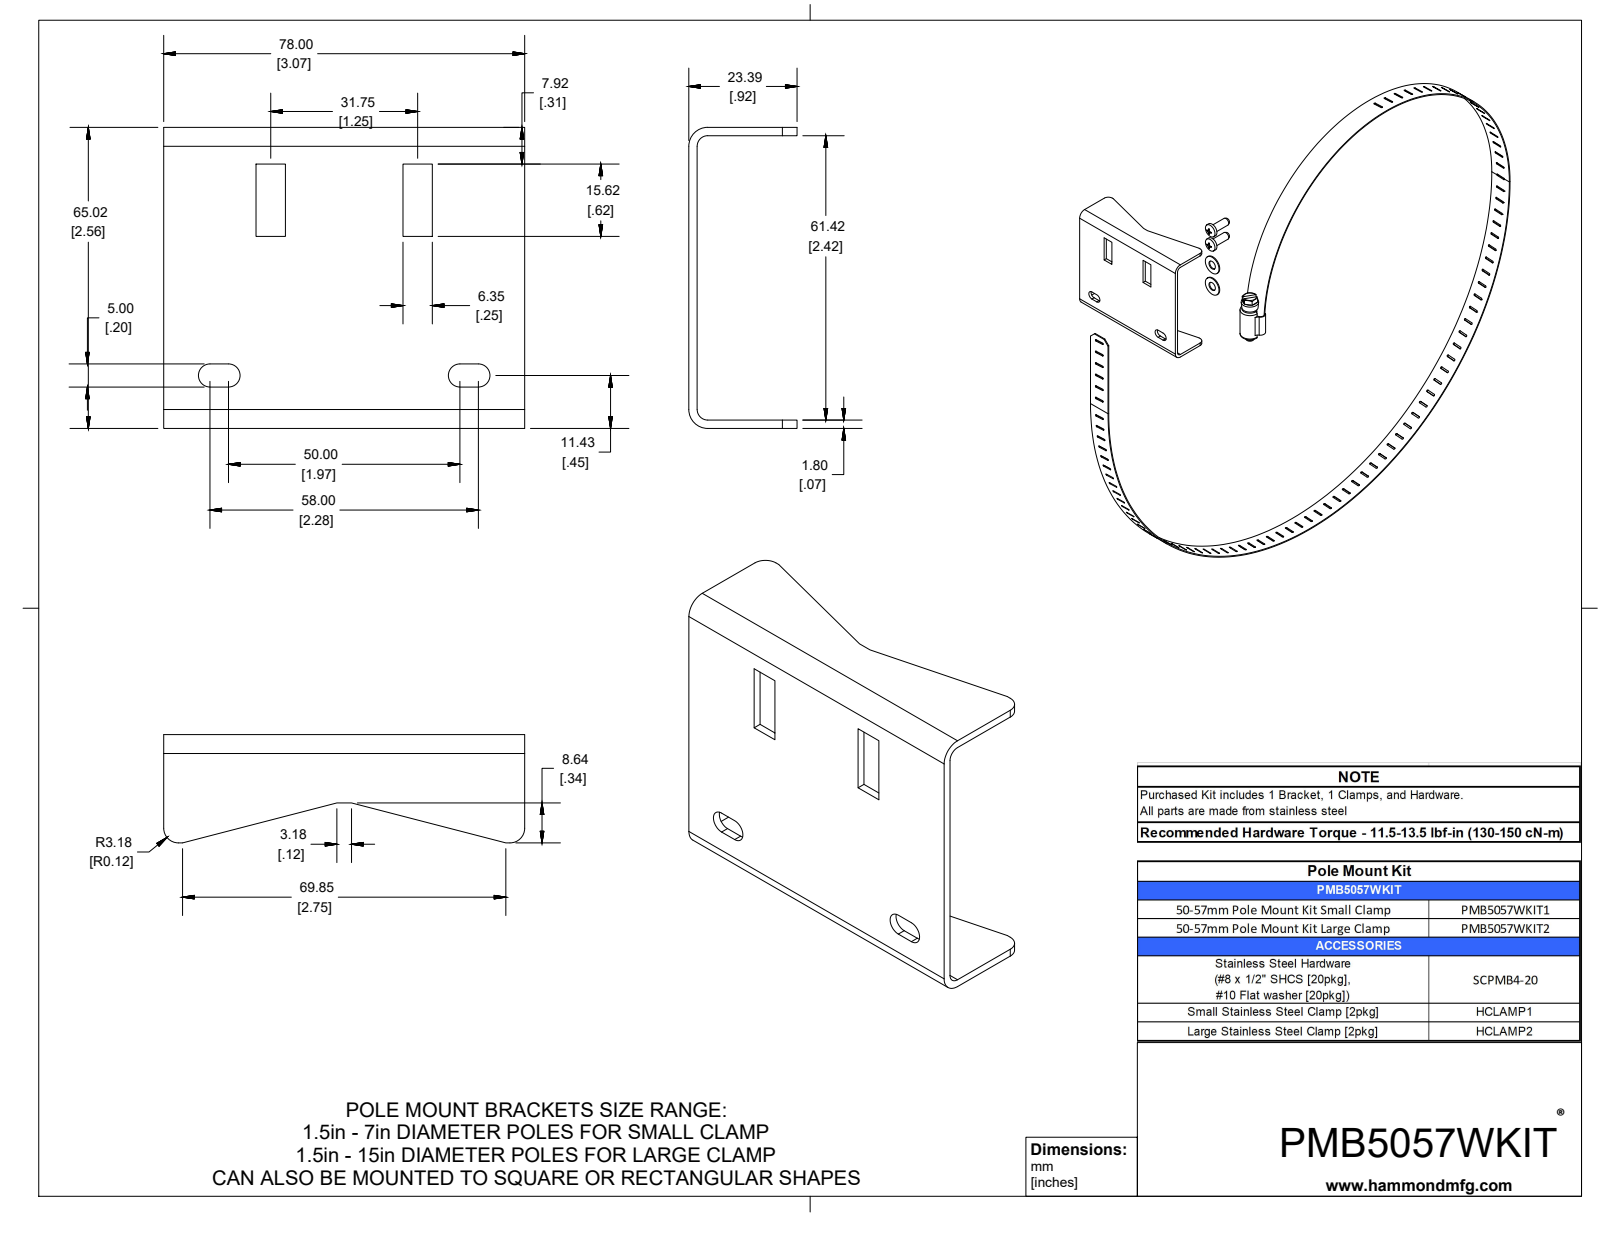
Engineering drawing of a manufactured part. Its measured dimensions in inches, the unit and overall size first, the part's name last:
Units: inches
Overall size (bounding box): 12.897 × 10.397 × 5.846
Round holes (diameter × count): ⌀0.205 ×2
Round bosses / shafts (diameter × count): ⌀0.438 ×2, ⌀0.176 ×2, ⌀0.313 ×1, ⌀0.22 ×1, ⌀0.2 ×1
Partial cylindrical surfaces — rounded edges, fillets, slot ends (radius × count): R0.02 ×182, R0.125 ×5, R0.098 ×4, R0.09 ×2, R0.1 ×2, R0.12 ×2, R0.161 ×2, R0.195 ×1
Main face-to-face distances: 0.071, 2.489, 2.418, 2.56, 4.937, 4.959, 4.866, 4.888, 0.022, 0.563
Hole centre spacings: 0.591
Volume: 1.37 in³ · Surface area: 69.48 in²
Bodies: 7 solids, 535 faces (296 planar, 218 cylindrical, 21 other)
Part name (STEP PRODUCT): PMB5057WKIT2
STEP written by: SolidWorks 2019 (CONFIG_CONTROL_DESIGN)
